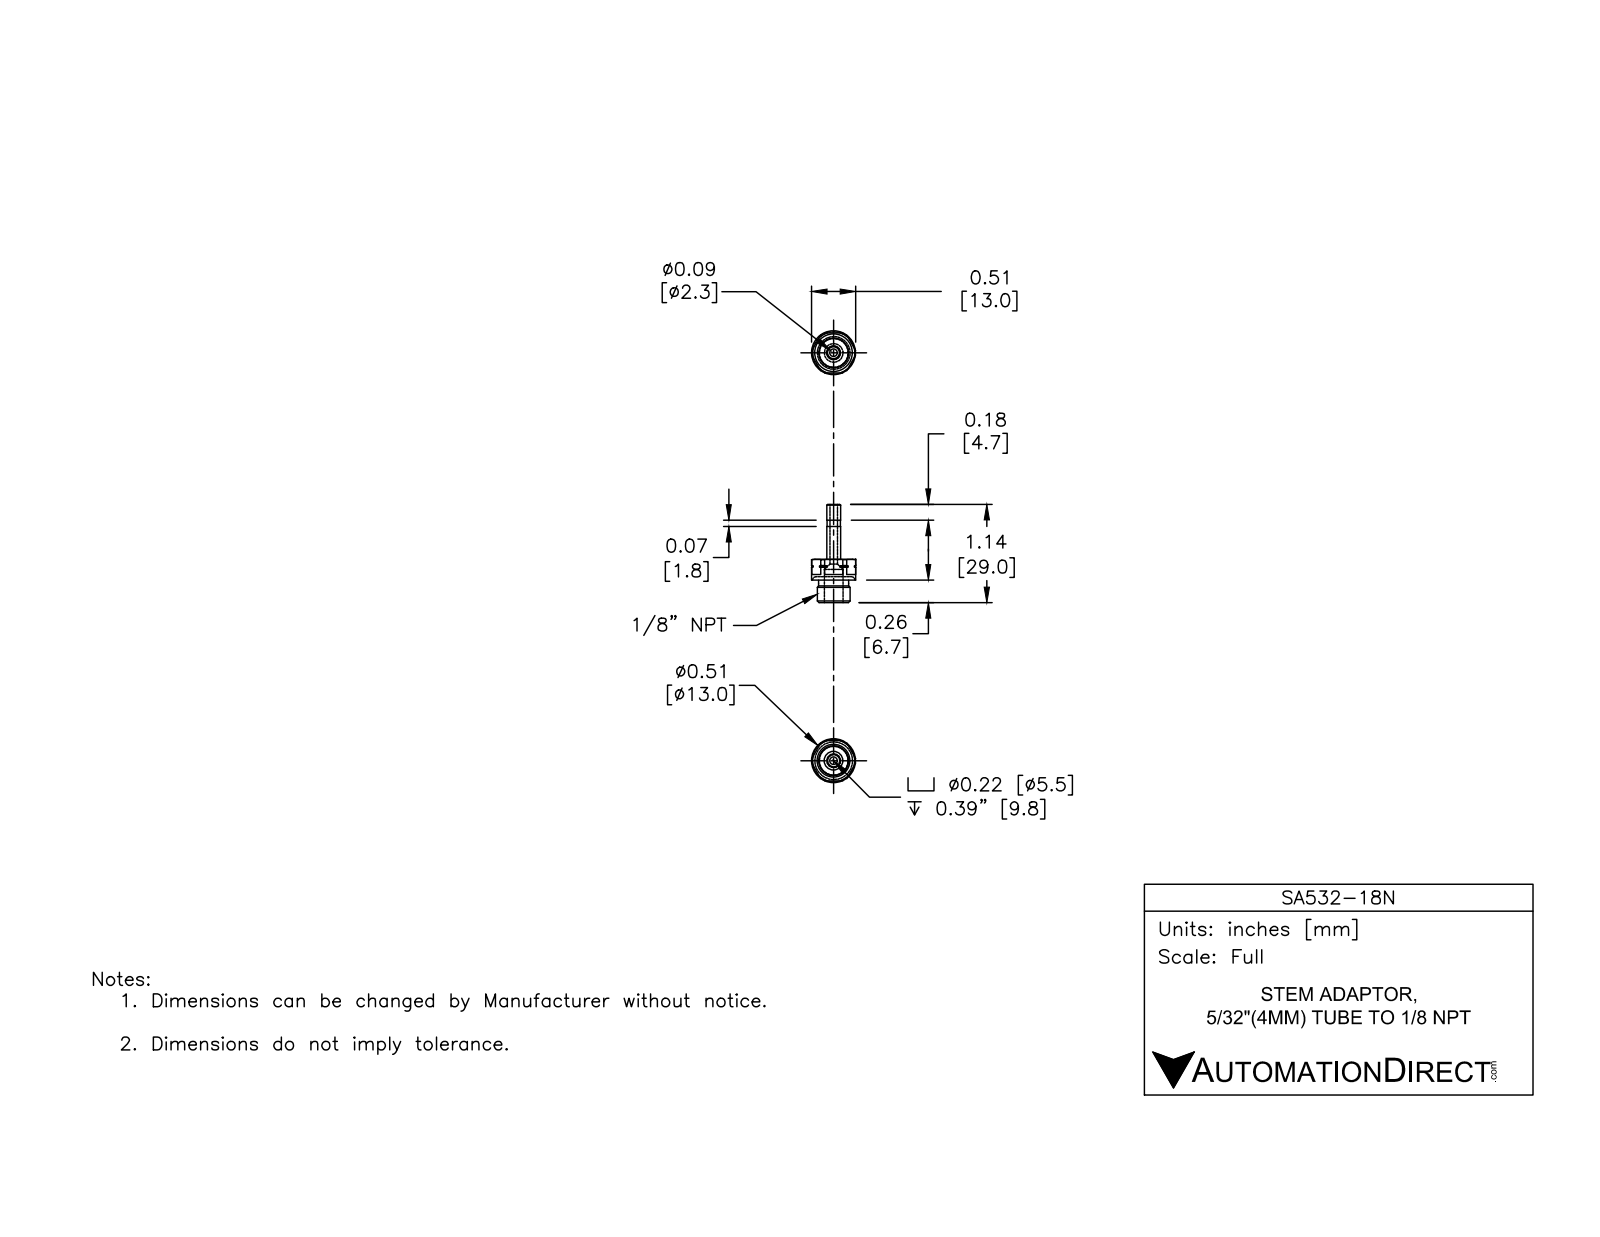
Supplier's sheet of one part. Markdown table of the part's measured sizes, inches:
| quantity | value |
| --- | --- |
| part name | SA532-18N |
| STEP written by | SolidWorks 2015 (CONFIG_CONTROL_DESIGN) |
| units | inches |
| bodies | 2 solids, 75 faces (18 planar, 29 cylindrical, 28 other) |
| overall size | 1.14 × 0.512 × 0.512 |
| volume | 0.073 in³ |
| surface area | 2.206 in² |
| round holes (diameter × count) | 0.089 × 1, 0.217 × 1 |
| round bosses / shafts (diameter × count) | 0.512 × 1, 0.38 × 1, 0.348 × 1, 0.16 × 1, 0.155 × 1 |
| partial cylindrical surfaces (radius × count) | 0.245 × 1 |
| main face-to-face distances | 0.241, 0.466, 0.262, 0.503, 0.467, 0.326, 0.064, 0.177, 1.14, 0.878 |
